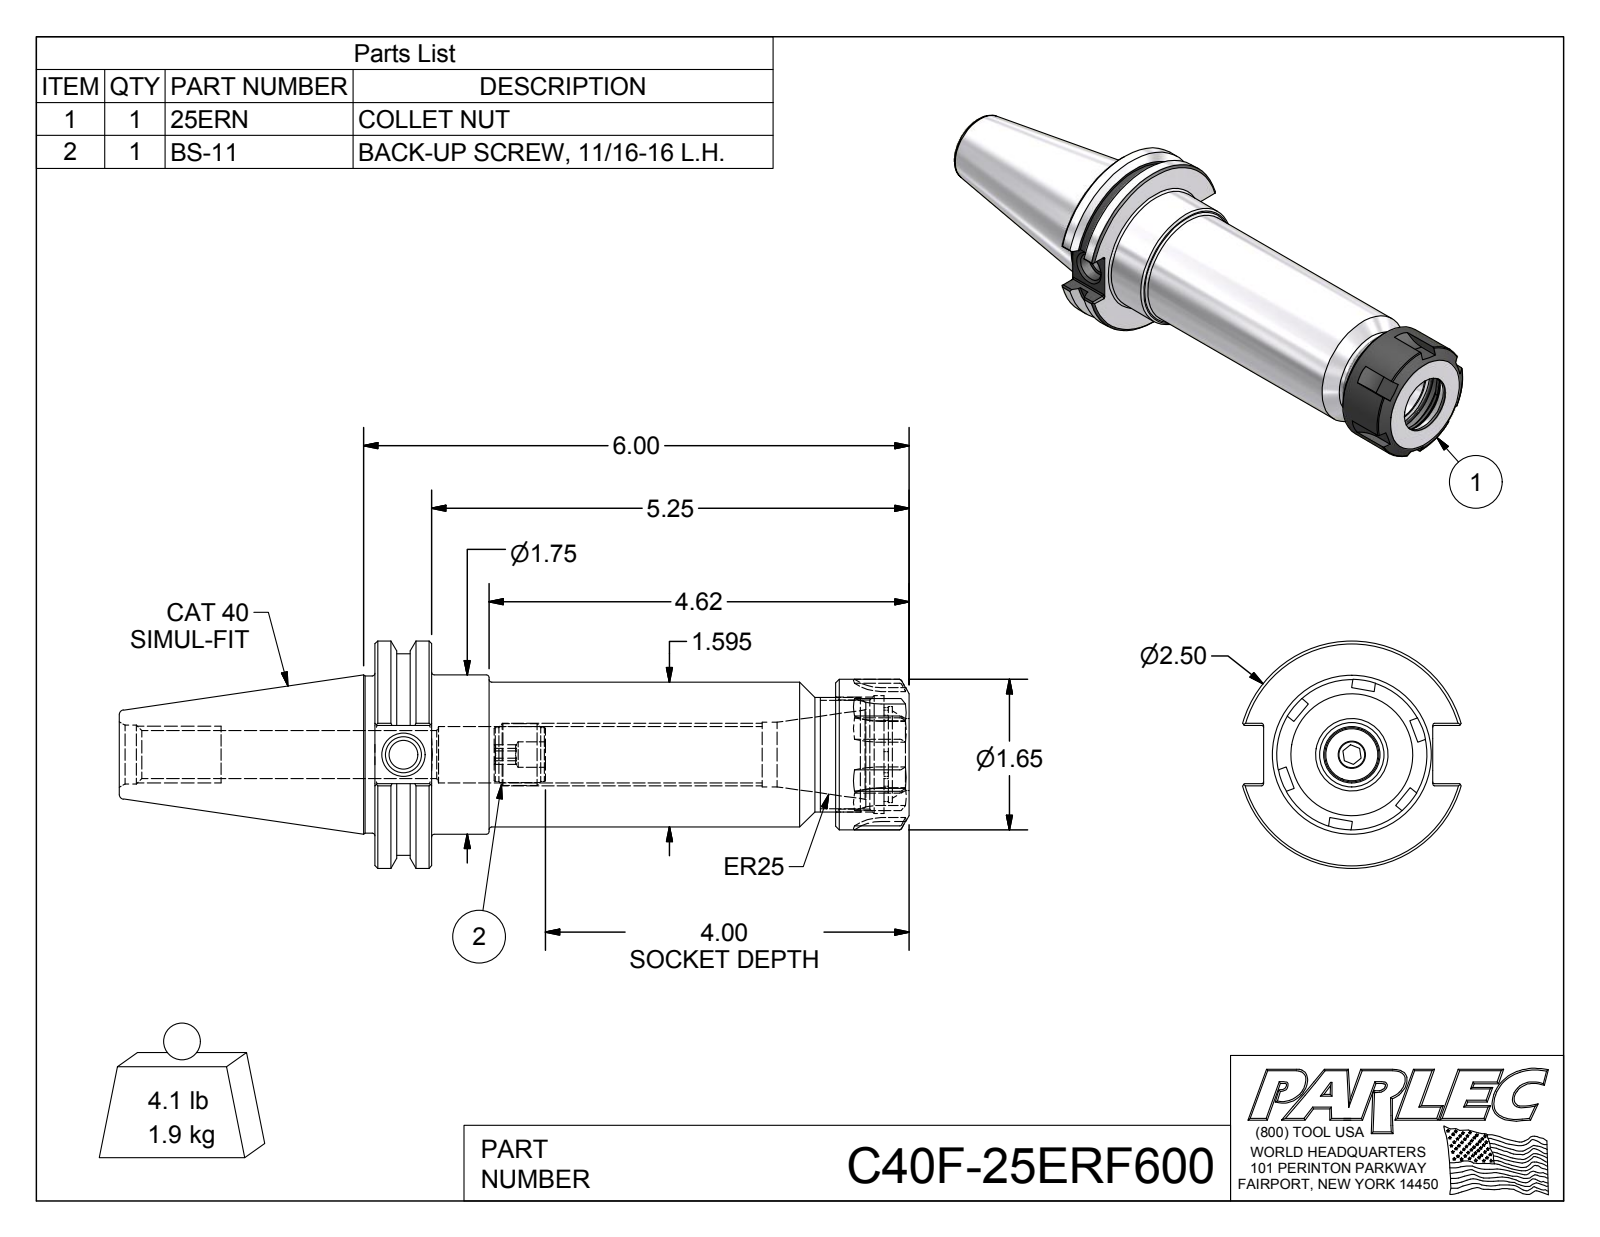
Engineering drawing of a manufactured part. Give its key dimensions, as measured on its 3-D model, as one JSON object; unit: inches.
{"part_name": "C40F-25ER6-1; 25ERN; BS-11; C40F-25ERF600", "step_written_by": "Autodesk Inventor 2016 (AUTOMOTIVE_DESIGN)", "units": "inches", "bodies": {"solids": 3, "faces": 187, "planar": 76, "cylindrical": 51, "other": 60}, "overall_size": [8.687, 2.5, 2.404], "volume_in3": 14.7, "surface_area_in2": 76.2, "round_holes": [[0.28, 1], [0.315, 1], [0.399, 1], [0.527, 1], [0.62, 1], [0.648, 1], [0.71, 1], [0.8, 1], [1.201, 1], [1.294, 1]], "round_bosses_or_shafts": [[2.5, 1], [2.219, 1], [1.75, 1], [1.73, 1], [1.654, 1], [1.595, 1], [1.26, 1], [0.681, 1]], "partial_cylinders_radius": [[0.02, 24], [0.472, 1], [0.514, 1], [0.529, 1]], "face_to_face_distances": [0.625, 5.875, 5.25, 5.065, 4.44, 0.81, 5.596, 4.97, 0.53, 0.28]}
